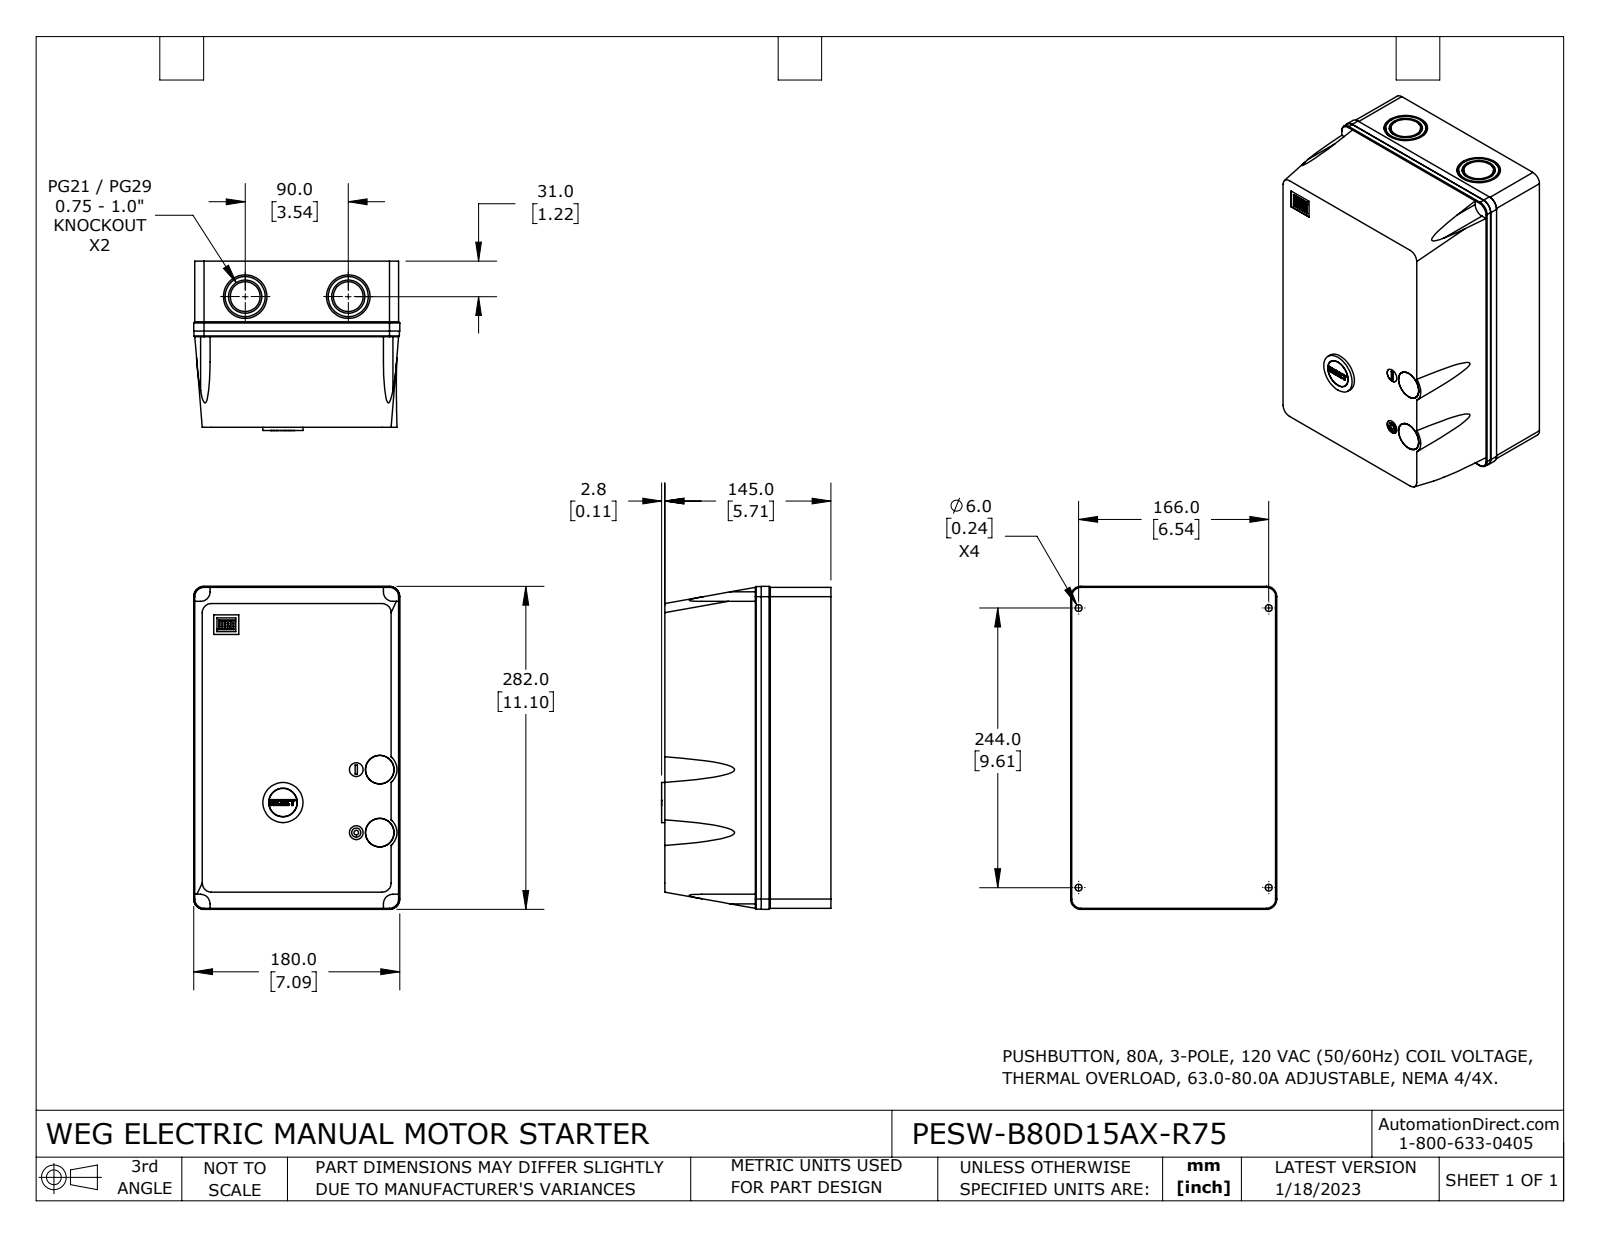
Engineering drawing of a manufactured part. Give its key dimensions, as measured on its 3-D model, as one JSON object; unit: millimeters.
{"part_name": "PESW-B80D15AX-R75", "step_written_by": "SolidWorks 2021 (CONFIG_CONTROL_DESIGN)", "units": "millimeters", "bodies": {"solids": 3, "faces": 286, "planar": 130, "cylindrical": 144, "other": 12}, "overall_size": [282, 180, 147.9], "volume_mm3": 7014000, "surface_area_mm2": 232257, "round_holes": [[6, 4], [25, 3], [12, 2], [29, 2], [38, 2], [4, 1], [30.5, 1]], "round_bosses_or_shafts": [[35, 3], [26, 2], [24.8, 2], [30.3, 1], [24.6, 1], [14, 1], [8, 1]], "partial_cylinders_radius": [[0.1, 34], [8, 4], [8.3, 4], [8.7, 4], [9, 4], [1.6, 1]], "face_to_face_distances": [145, 178, 280, 1, 0.7, 179, 179.7, 178.7, 281, 180], "hole_center_spacings": [20.5, 55, 58.7, 166, 244, 295.11, 49.14, 57.14]}
